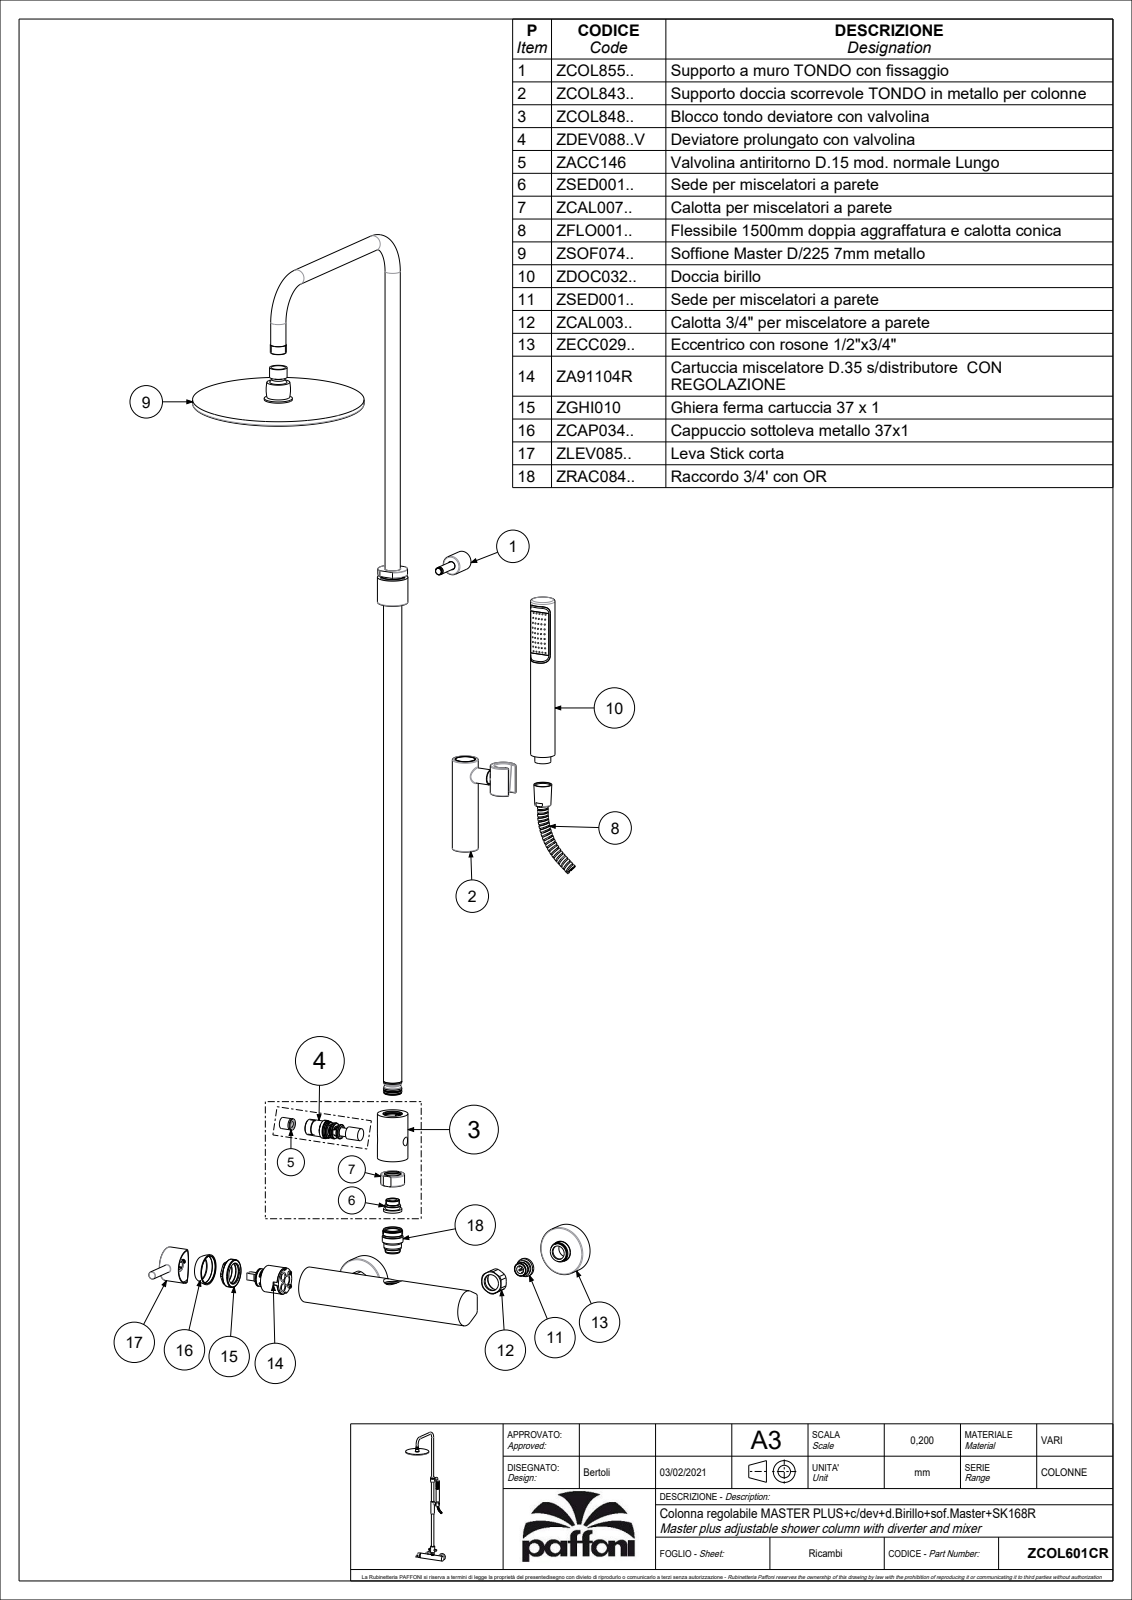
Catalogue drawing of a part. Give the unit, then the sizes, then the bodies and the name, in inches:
Units: inches
Overall size (bounding box): 51.209 × 19.343 × 10.775
Round holes (diameter × count): ⌀0.047 ×80, ⌀0.059 ×45, ⌀0.197 ×7, ⌀0.413 ×4, ⌀0.669 ×4, ⌀0.984 ×4, ⌀0.138 ×3, ⌀0.276 ×3, ⌀0.394 ×3, ⌀0.63 ×3, ⌀0.13 ×2, ⌀0.177 ×2
Round bosses / shafts (diameter × count): ⌀0.945 ×4, ⌀0.787 ×4, ⌀0.906 ×3, ⌀0.827 ×3, ⌀2.5 ×2, ⌀1.102 ×2, ⌀1.063 ×2, ⌀0.728 ×2
Partial cylindrical surfaces — rounded edges, fillets, slot ends (radius × count): R0.059 ×45, R0.012 ×24, R0.02 ×8, R0.039 ×6, R0.051 ×2, R0.197 ×2, R0.307 ×2, R0.386 ×2
Main face-to-face distances: 0.256, 0.146, 0.024, 0.138, 1.173, 1.15, 0.559, 0.413, 1.012, 1.035
Hole centre spacings: 0.311, 0.542, 1.109, 3.543, 0.256, 0.788, 0.512, 3.217
Volume: 56.38 in³ · Surface area: 923.7 in²
Bodies: 12 solids, 2156 faces (675 planar, 789 cylindrical, 692 other)
Part name (STEP PRODUCT): ZCOL601CR
STEP written by: CREO PARAMETRIC BY PTC INC, 2020044 (CONFIG_CONTROL_DESIGN)
